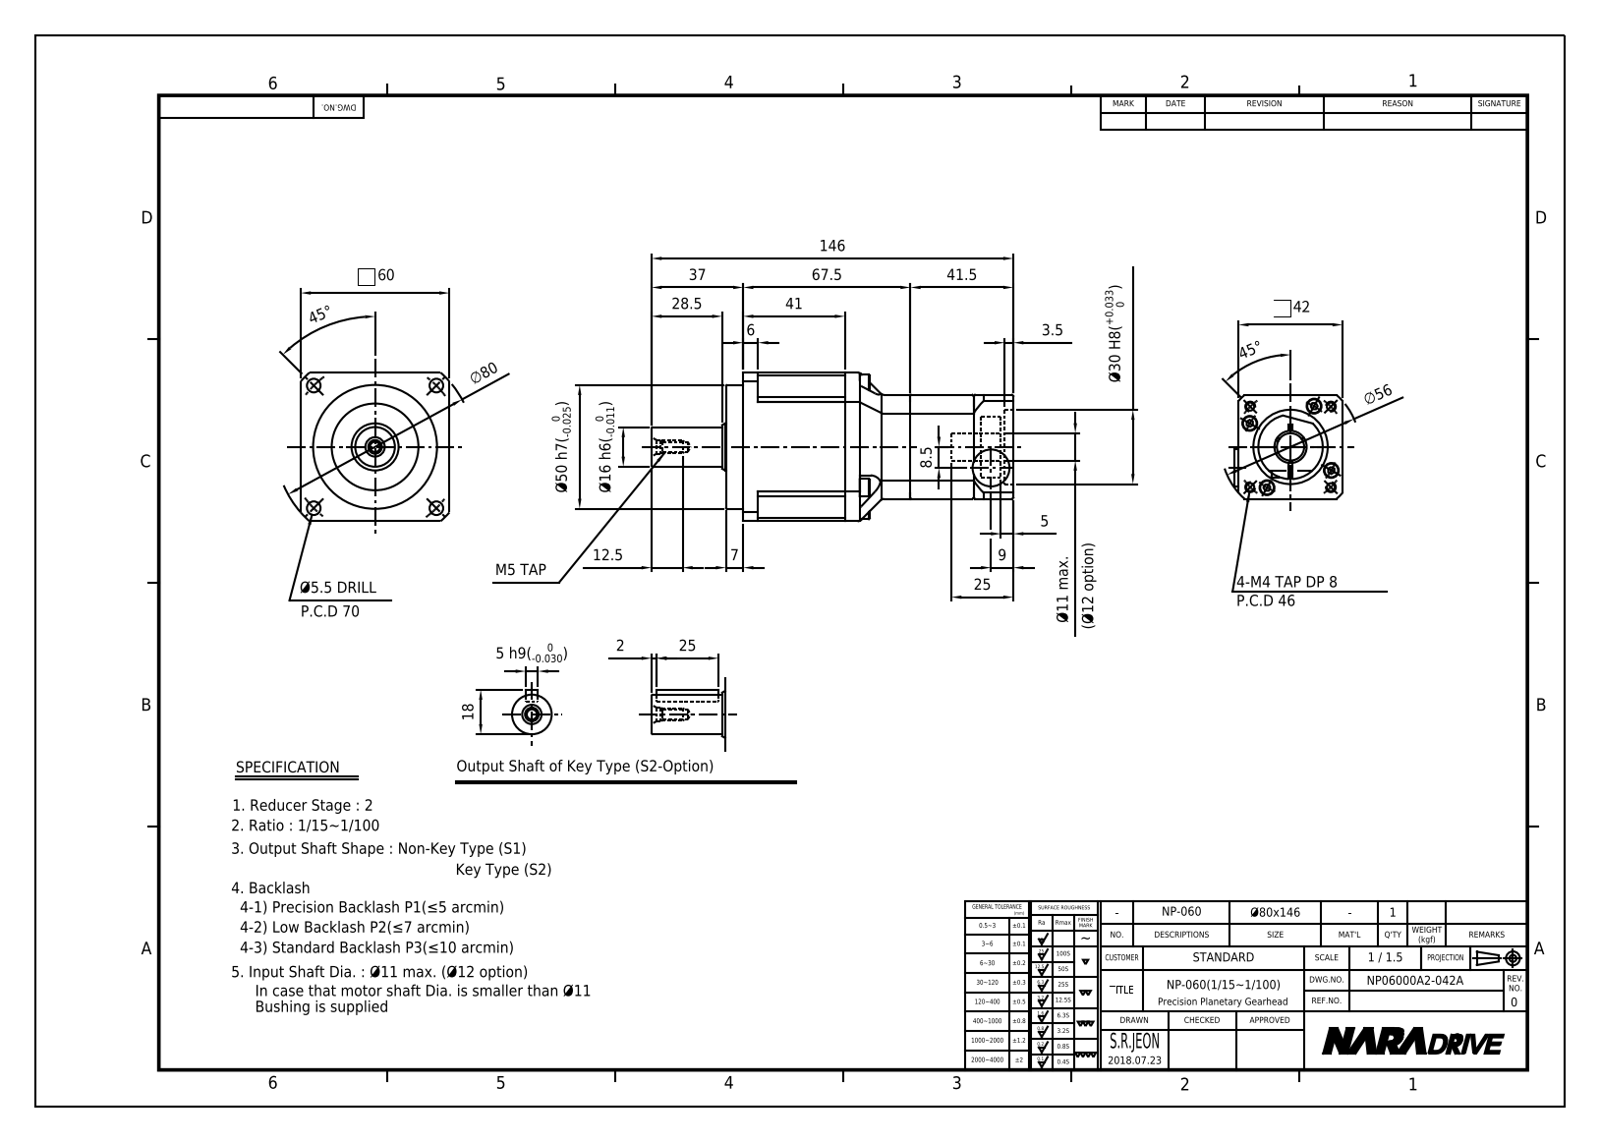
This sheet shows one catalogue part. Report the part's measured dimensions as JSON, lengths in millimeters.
{"part_name": "NP06000A2-042A-S1", "step_written_by": "Autodesk Inventor 2015 (AUTOMOTIVE_DESIGN)", "units": "millimeters", "bodies": {"solids": 1, "faces": 440, "planar": 208, "cylindrical": 119, "other": 113}, "overall_size": [146, 60, 60], "volume_mm3": 241145, "surface_area_mm2": 49491, "round_holes": [[2.46, 9], [3.4, 9], [3.24, 8], [6, 8], [4.2, 4], [5.5, 4], [4.13, 1], [7, 1], [8.5, 1], [11, 1], [13, 1], [27, 1]], "round_bosses_or_shafts": [[5.5, 5], [3, 5], [7, 4], [4, 4], [50, 1], [35, 1], [26, 1], [19, 1]], "partial_cylinders_radius": [[2, 8], [7, 8], [3, 1], [28, 1], [35, 1], [40, 1]], "face_to_face_distances": [51, 9, 60, 42, 5, 7, 46, 39, 44, 71], "hole_center_spacings": [41.88, 36.68, 9.39, 12, 19, 23, 34.27, 38.57]}
